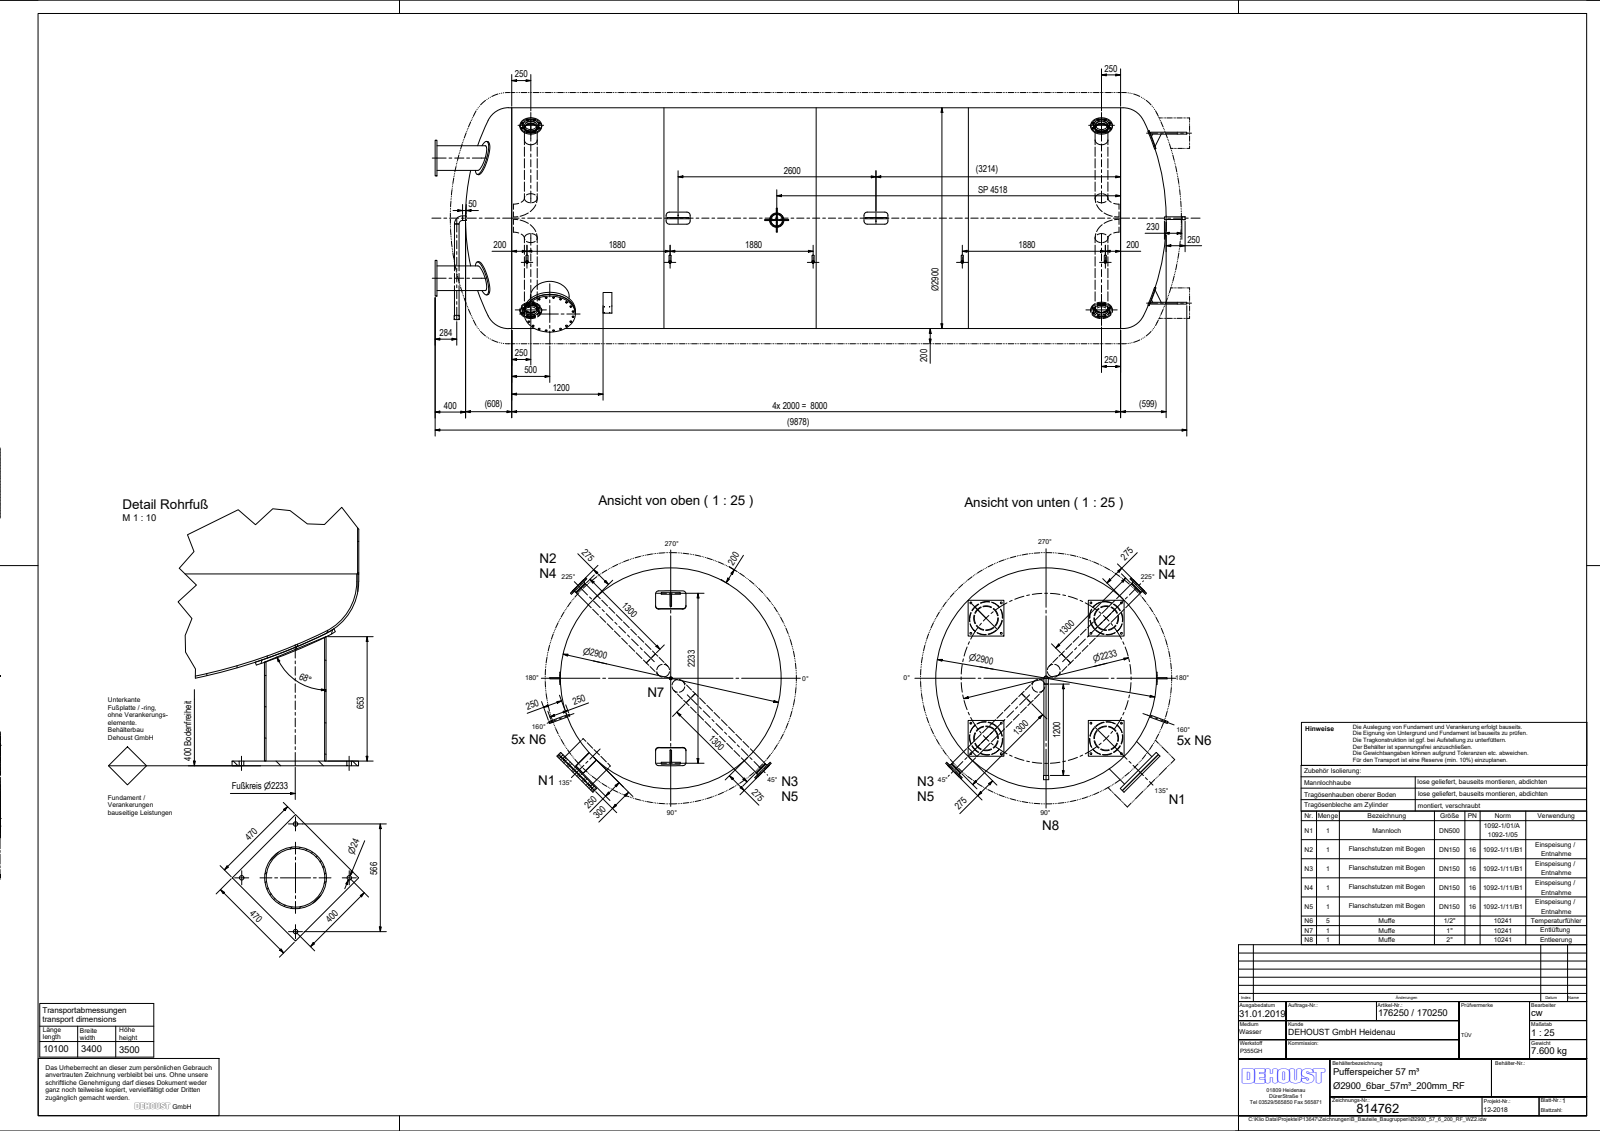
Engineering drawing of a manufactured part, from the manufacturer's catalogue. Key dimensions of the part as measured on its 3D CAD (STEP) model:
Part name (STEP PRODUCT): Ø2900_57_6_200_RF_WZ2; Klöpper_Gew_Ø2900_8,3; Klöpper_Gew_Ø2900_10,3; Zyl_Ø2900_6x8000_2019 (+8 more)
STEP written by: Autodesk Inventor 2019 (AUTOMOTIVE_DESIGN)
Units: millimetres
Bodies: 58 solids, 449 faces (178 planar, 225 cylindrical, 46 other)
Overall size (bounding box): 9878.11 × 3051.99 × 2946.24
Volume: 894 900 000 mm³ · Surface area: 201 900 000 mm²
Round holes (diameter × count): ⌀26 ×36, ⌀22 ×32, ⌀24 ×16, ⌀159.3 ×8, ⌀18.63 ×5, ⌀21.7 ×5, ⌀26.9 ×5, ⌀5.8 ×4, ⌀168.3 ×4, ⌀307.9 ×4, ⌀5 ×2, ⌀52.3 ×2
Round bosses / shafts (diameter × count): ⌀168.3 ×8, ⌀26.9 ×5, ⌀26.4 ×5, ⌀450 ×4, ⌀323.9 ×4, ⌀285 ×4, ⌀212 ×4, ⌀2900 ×1
Partial cylindrical surfaces — rounded edges, fillets, slot ends (radius × count): R42 ×16, R10 ×6, R6 ×4, R5 ×2, R36 ×2, R72 ×2, R125 ×1, R1460 ×1
Main face-to-face distances: 25, 600, 4732.96, 5282.96, 4707.96, 5257.96, 550, 27.99, 3725, 4275
Hole centre spacings: 120, 310, 191.59, 501.59, 7500, 169.71, 438.41, 1880
